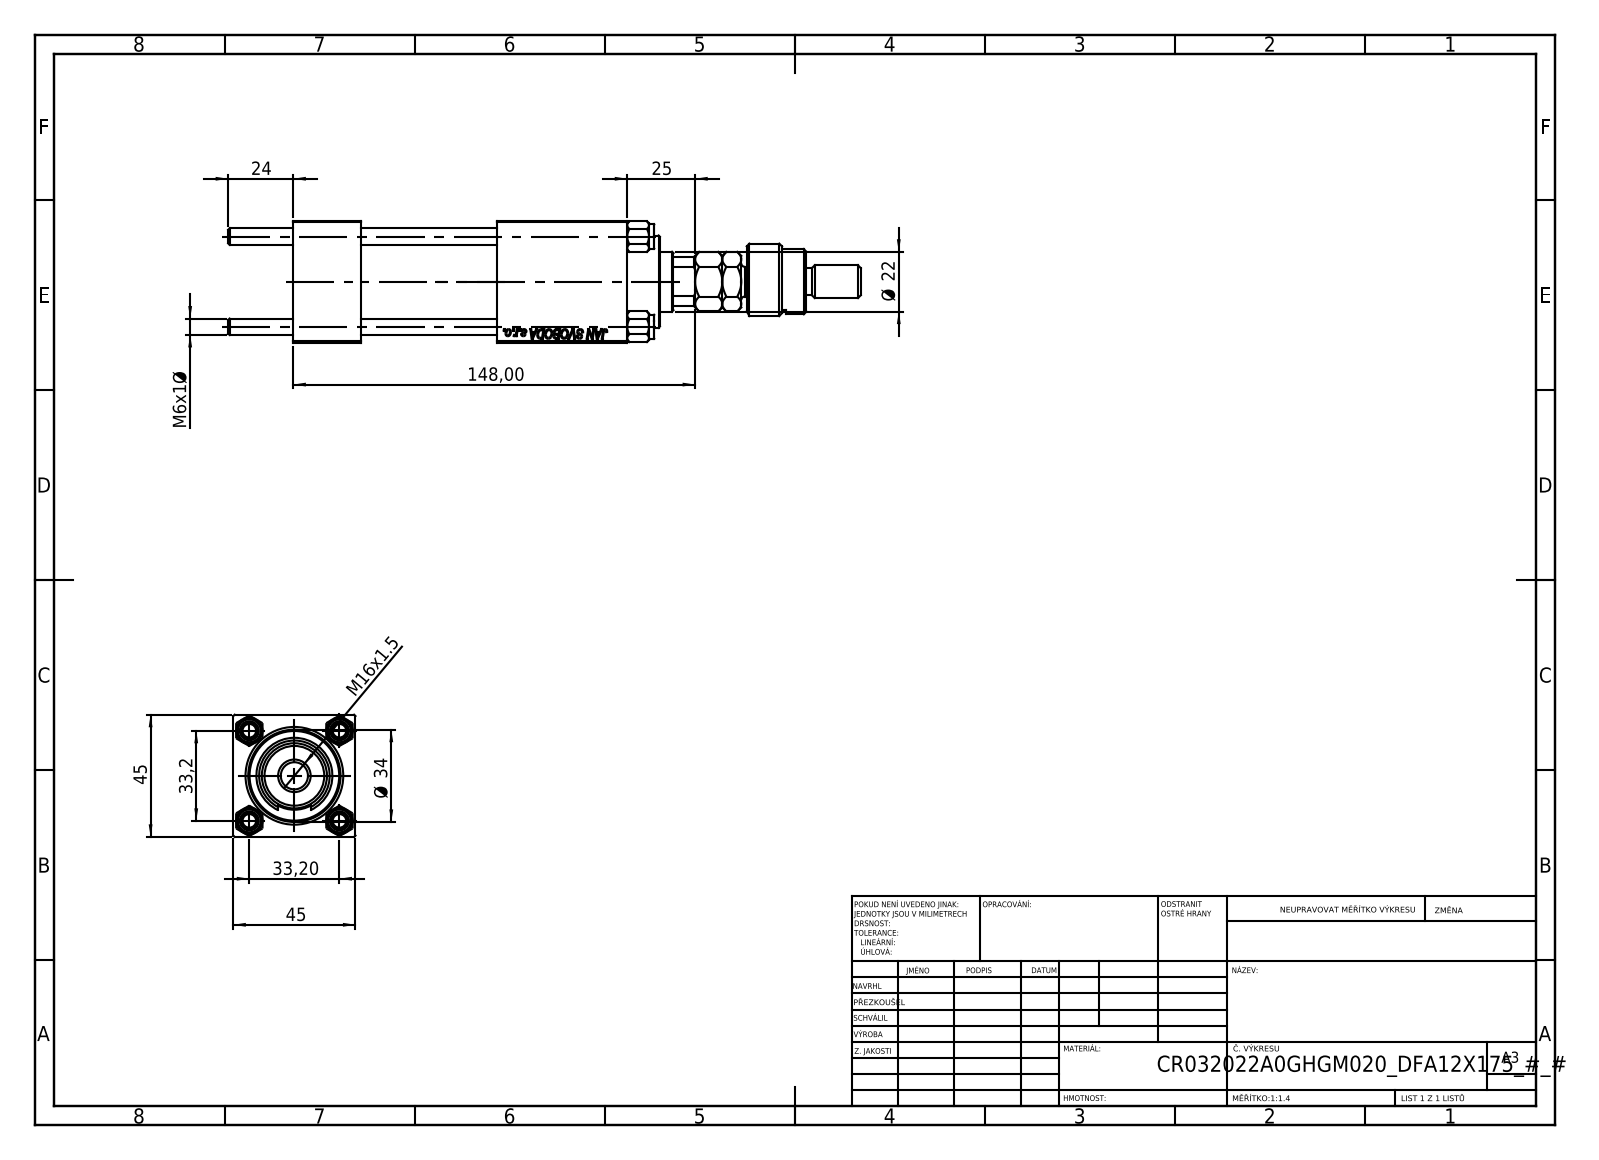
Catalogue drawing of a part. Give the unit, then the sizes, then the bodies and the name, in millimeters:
Units: millimetres
Overall size (bounding box): 233 × 45 × 45
Round holes (diameter × count): ⌀6 ×4, ⌀7 ×2, ⌀13.16 ×2, ⌀20 ×2, ⌀10.5 ×1, ⌀22 ×1, ⌀24 ×1, ⌀25 ×1, ⌀32 ×1, ⌀33 ×1
Round bosses / shafts (diameter × count): ⌀9 ×4, ⌀38 ×1, ⌀34 ×1, ⌀28 ×1, ⌀18 ×1, ⌀12 ×1, ⌀11 ×1, ⌀10 ×1
Partial cylindrical surfaces — rounded edges, fillets, slot ends (radius × count): R9.75 ×1, R10.5 ×1
Main face-to-face distances: 45, 25, 123, 50, 98, 48, 75, 94.3, 69.3, 19.3
Hole centre spacings: 23.48, 33.2, 46.95, 75.5
Volume: 232 154 mm³ · Surface area: 84 163 mm²
Bodies: 13 solids, 1218 faces (547 planar, 91 cylindrical, 580 other)
Part name (STEP PRODUCT): V215CR_VCP; V215CR_BODY_A; V215_VC_A; MFA (+3 more)
STEP written by: SolidWorks 2019 (CONFIG_CONTROL_DESIGN)
